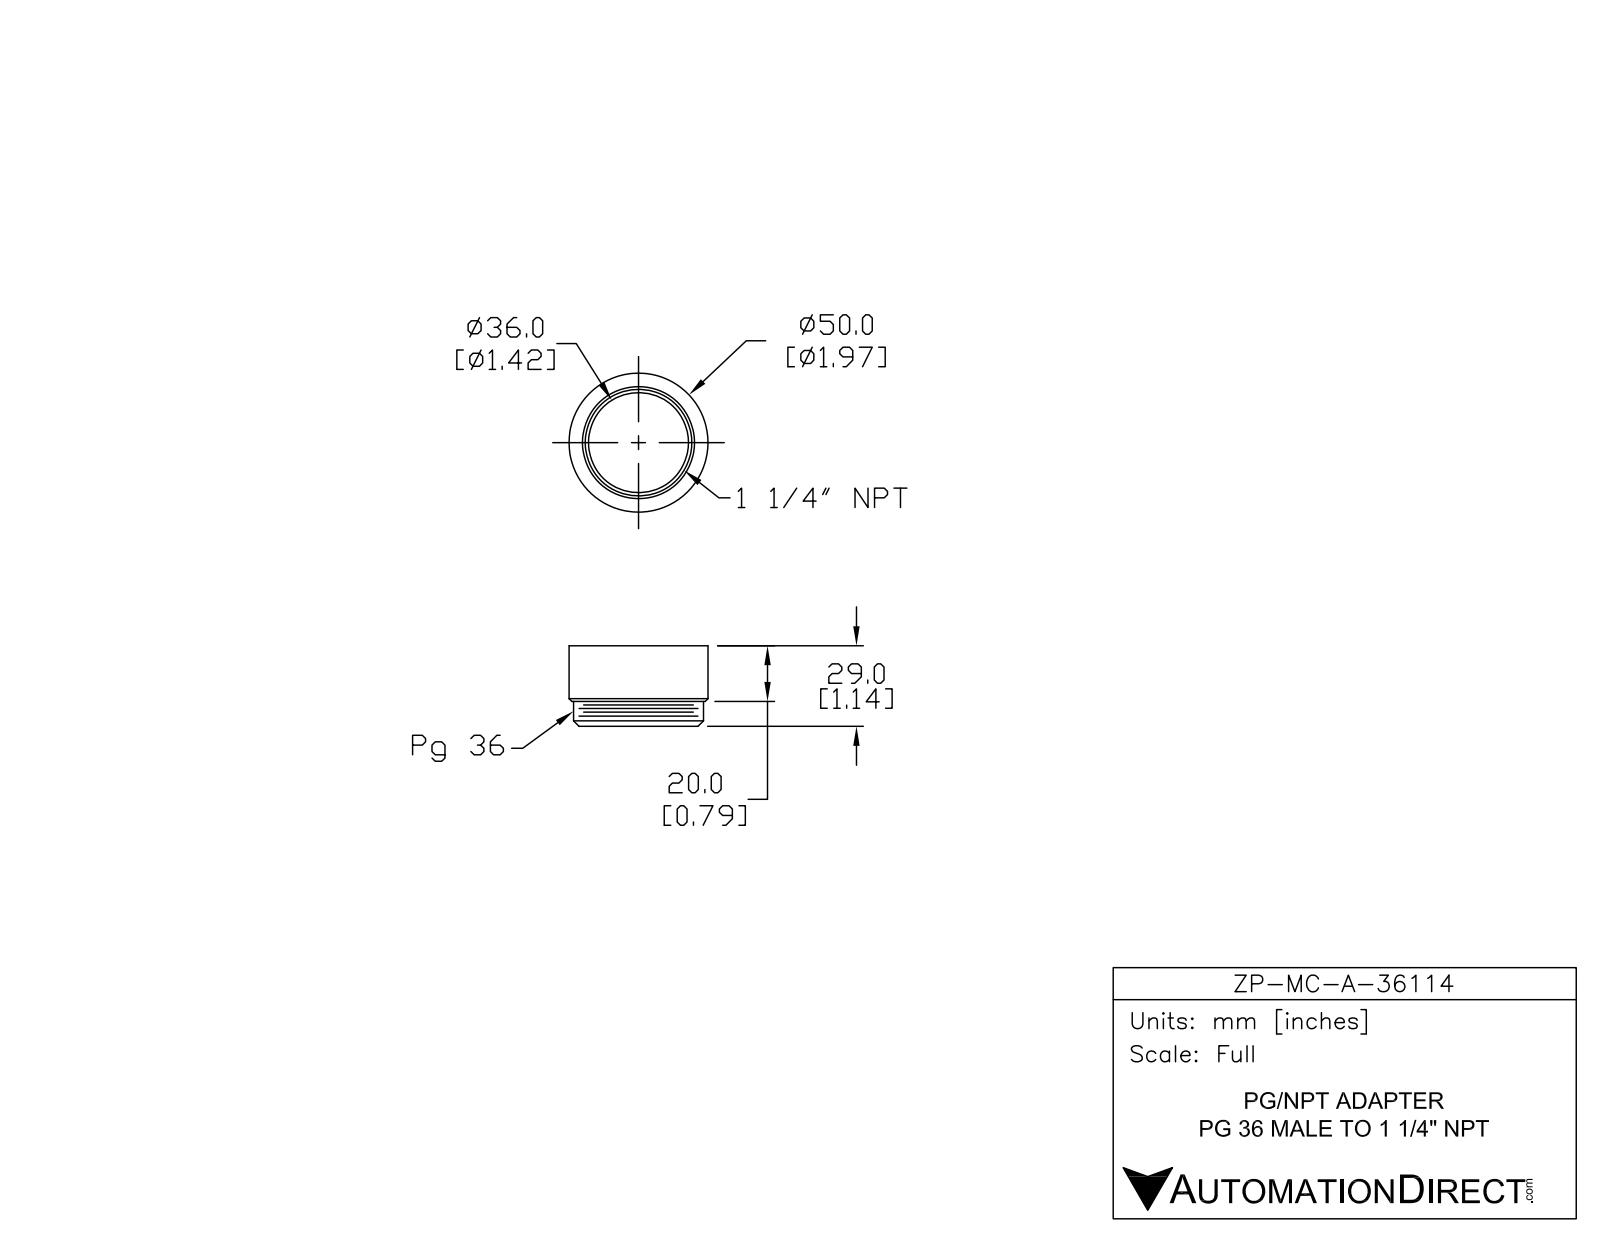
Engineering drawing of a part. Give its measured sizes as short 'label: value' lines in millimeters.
name: ZP-MC-A-36114
written by: SolidWorks 2014 (AUTOMOTIVE_DESIGN)
unit: mm
bodies: 1 solid, 18 faces (4 planar, 8 cylindrical, 6 other)
size: 50 × 50 × 29
volume: 22 411 mm³; area: 9 420 mm²
holes: 1× ⌀36, 1× ⌀38.36
bosses: 1× ⌀50, 1× ⌀46.78
face distances: 29, 12, 17, 9.17, 2.83, 19.83
